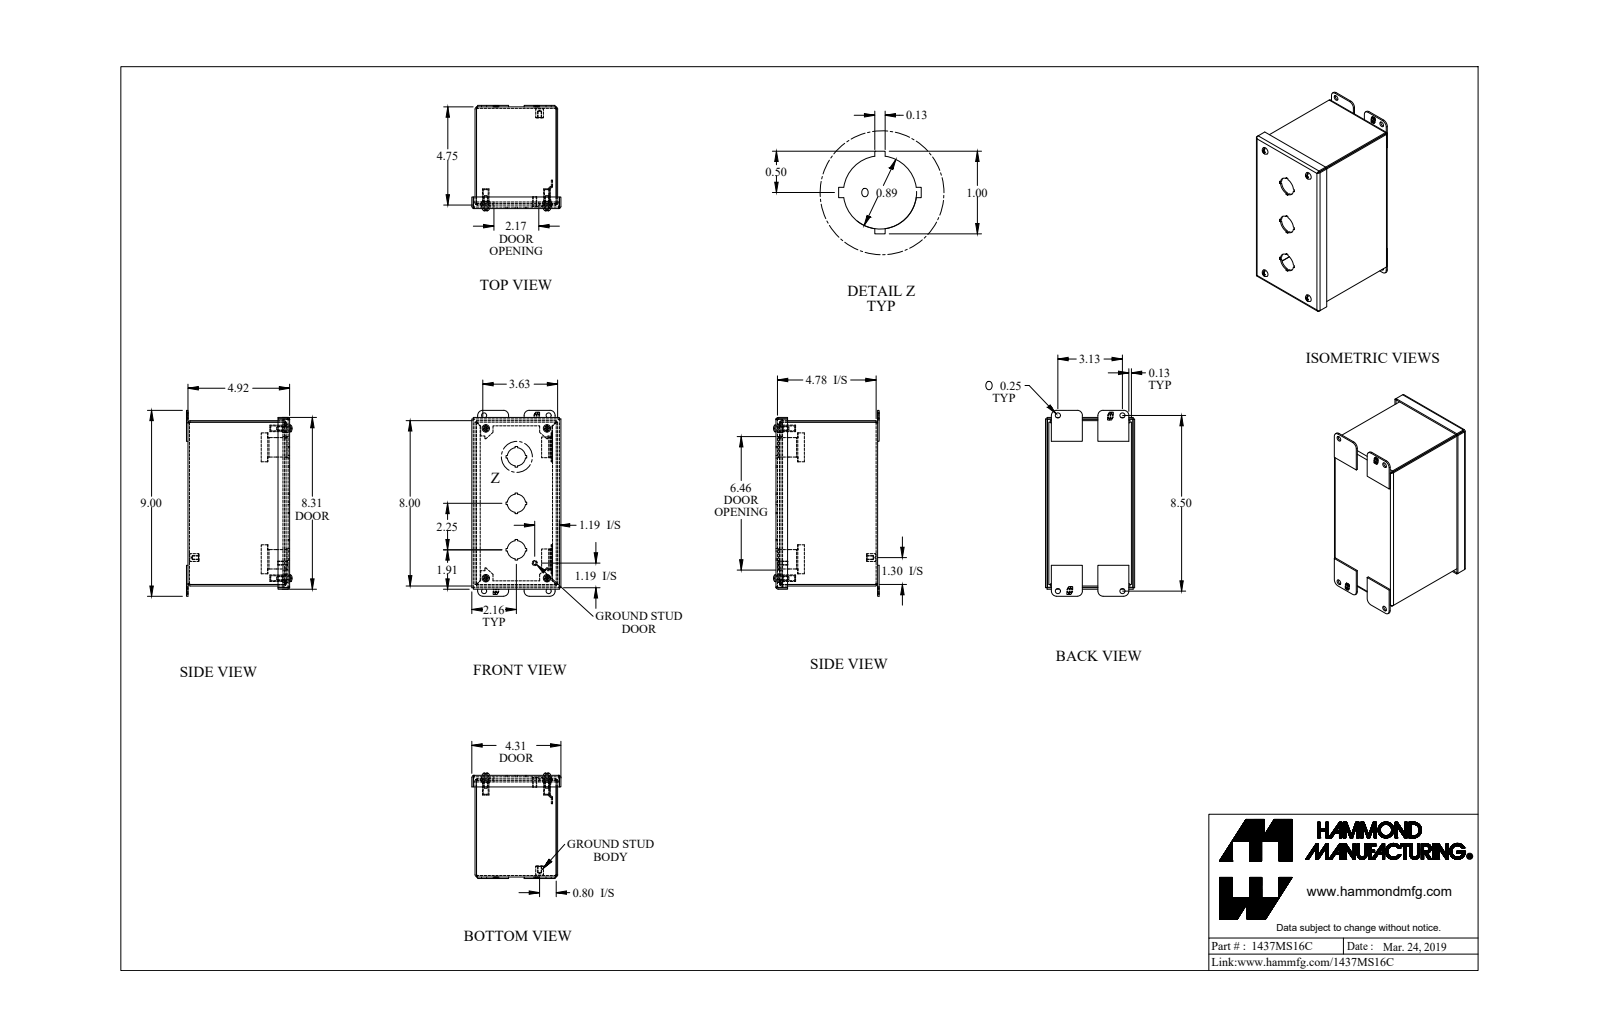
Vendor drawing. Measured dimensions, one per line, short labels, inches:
name: 1437MS16C_Default
written by: SolidWorks 2019 (CONFIG_CONTROL_DESIGN)
unit: in
bodies: 23 solids, 653 faces (459 planar, 164 cylindrical, 30 other)
size: 9 × 5.104 × 4.312
volume: 17.1 in³; area: 457.9 in²
holes: 8× ⌀0.25, 4× ⌀0.065, 4× ⌀0.239, 4× ⌀0.253, 4× ⌀0.406, 3× ⌀0.886, 1× ⌀0.156
bosses: 5× ⌀0.19, 4× ⌀0.406, 4× ⌀0.315, 4× ⌀0.148, 1× ⌀0.375, 1× ⌀0.25
rounds: 12× R0.036, 12× R0.108, 8× R0.25, 4× R0.029, 4× R0.086, 4× R0.125, 4× R0.171
face distances: 0.072, 3.928, 4.85, 4.922, 4, 3.856, 7.928, 4.778, 0.156, 8
hole spacings: 7.25, 7.876, 0.63, 2.961, 3.107, 3.916, 6.059, 7.832
